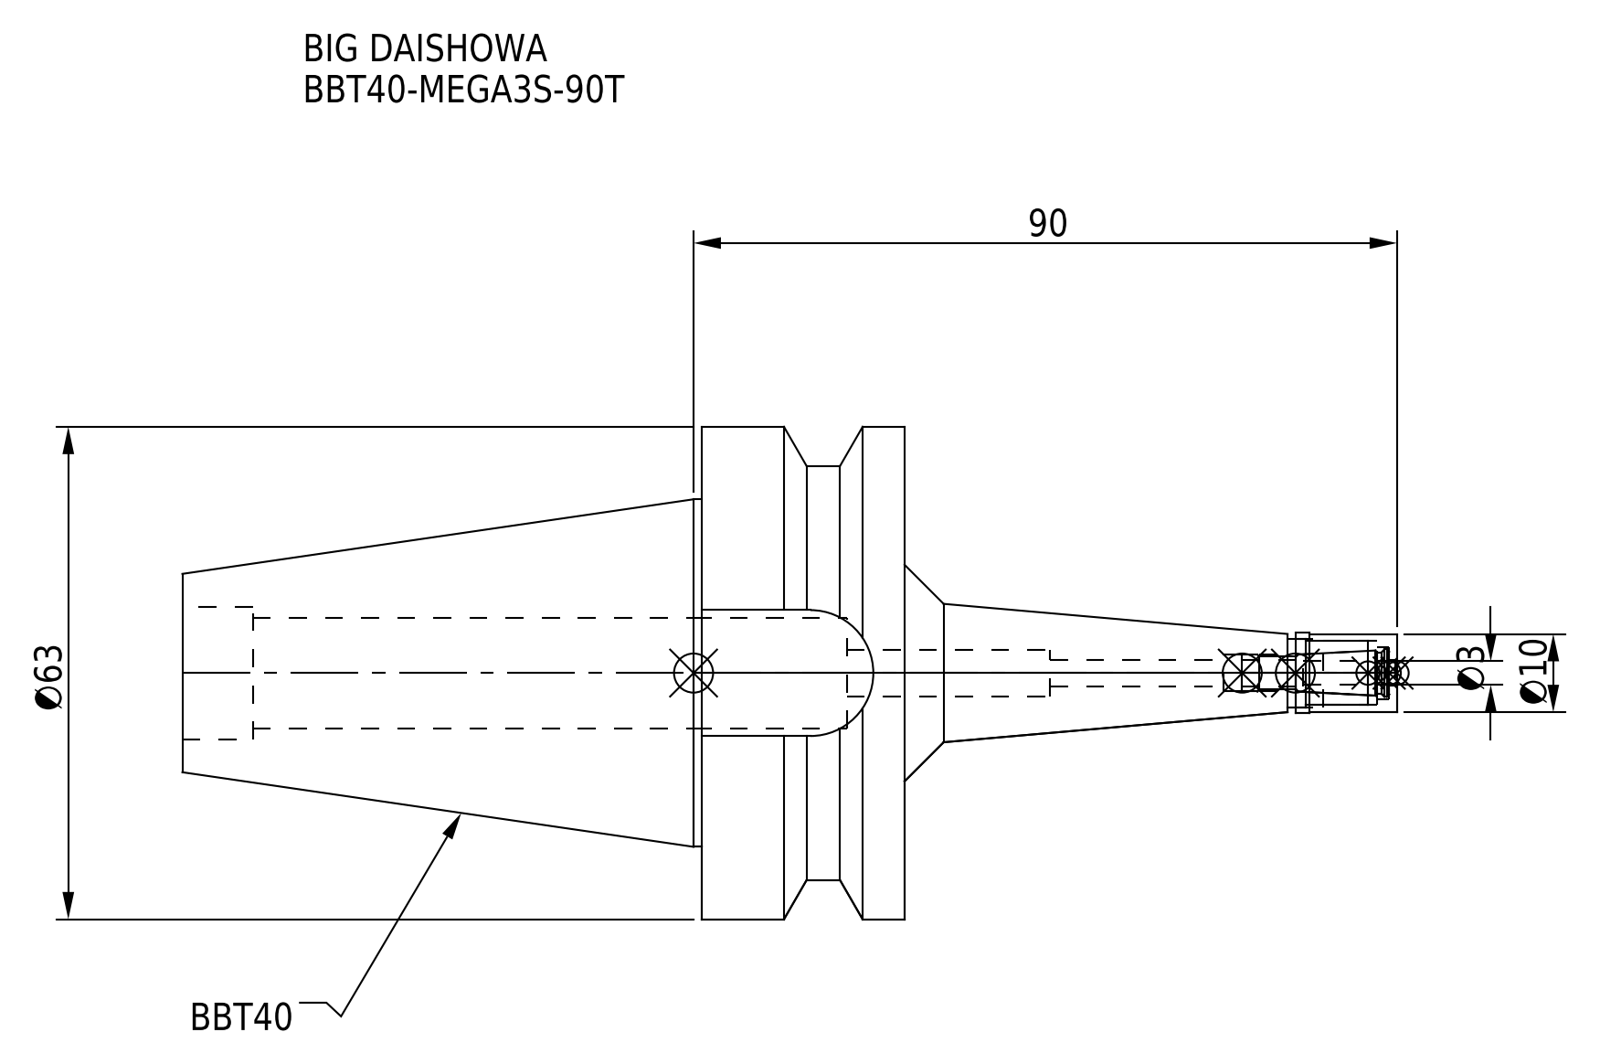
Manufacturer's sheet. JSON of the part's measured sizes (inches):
{"part_name": "BBT40-MEGA3S-90T-030.stp; DXF_TEMP_ASSY_ASM_4_ASM.stp; MGN3S_1.stp; BBT40-MEGA3S-90T_1.stp (+3 more)", "step_written_by": "SolidWorks 2019 (CONFIG_CONTROL_DESIGN)", "units": "inches", "bodies": {"solids": 2, "faces": 74, "planar": 22, "cylindrical": 38, "other": 14}, "overall_size": [6.118, 2.48, 2.48], "volume_in3": 7.934, "surface_area_in2": 41.41, "round_holes": [[0.13, 1], [0.134, 1], [0.185, 1], [0.236, 1], [0.26, 1], [0.323, 1], [0.343, 1], [0.559, 1], [0.669, 1]], "round_bosses_or_shafts": [[2.48, 1], [2.087, 1], [1.75, 1], [0.406, 1], [0.394, 1]], "partial_cylinders_radius": [[0.317, 1]], "face_to_face_distances": [1.024, 1.772, 3.638, 2.614, 0.634, 0.732, 0.291, 3.346, 2.26, 2.992]}
